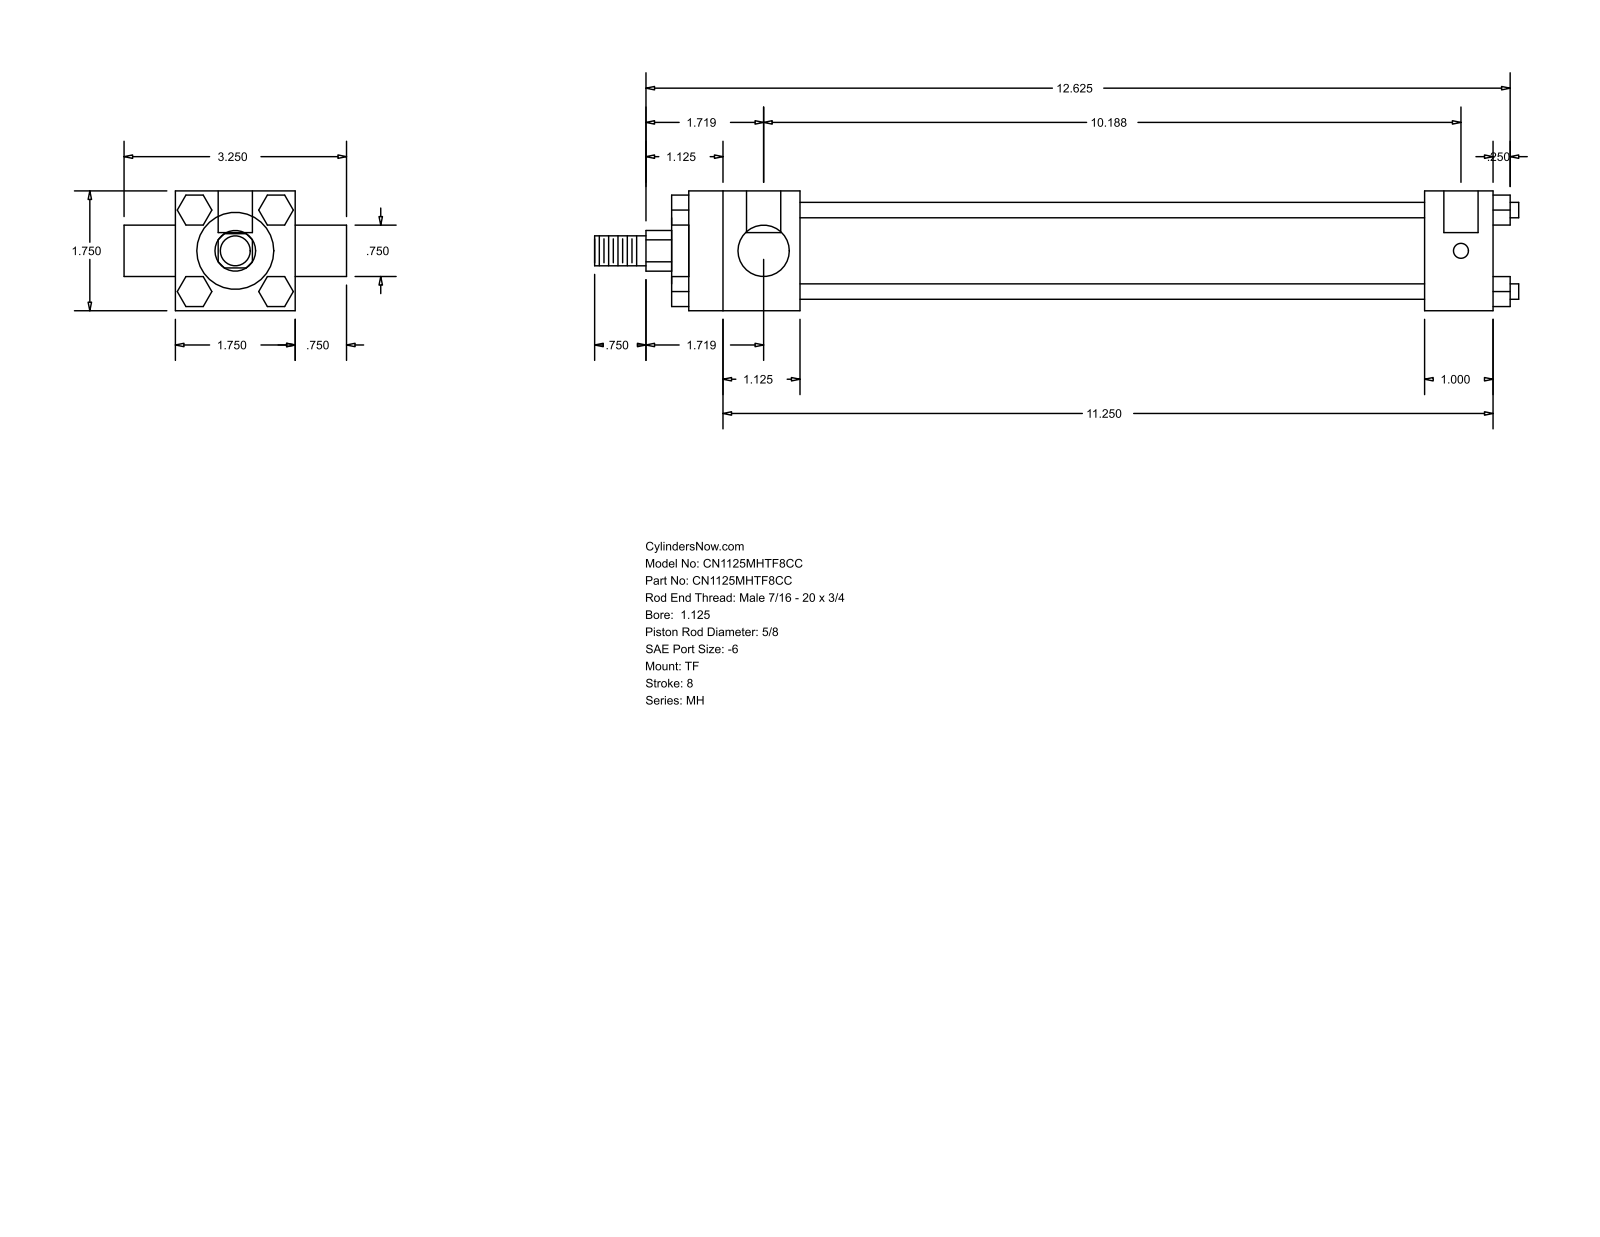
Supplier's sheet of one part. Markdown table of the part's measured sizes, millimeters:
| quantity | value |
| --- | --- |
| part name | MH_TF__0112_0.625 |
| STEP written by | GSSL Pune (CONFIG_CONTROL_DESIGN) |
| units | millimeters |
| bodies | 0 solids, 120 faces (92 planar, 28 cylindrical, 0 other) |
| overall size | 342.9 × 82.55 × 44.45 |
| round holes (diameter × count) | 5.56 × 3, 12.7 × 2 |
| round bosses / shafts (diameter × count) | 5.71 × 4, 34.92 × 1, 28.57 × 1, 19.05 × 1, 15.88 × 1, 11.11 × 1 |
| partial cylindrical surfaces (radius × count) | 7.54 × 1 |
| main face-to-face distances | 44.46, 11.11, 231.78, 257.17, 25.39, 41.27, 273.05, 298.44, 47.62, 6.35 |
| hole center spacings | 3.17, 255.59, 258.76 |
